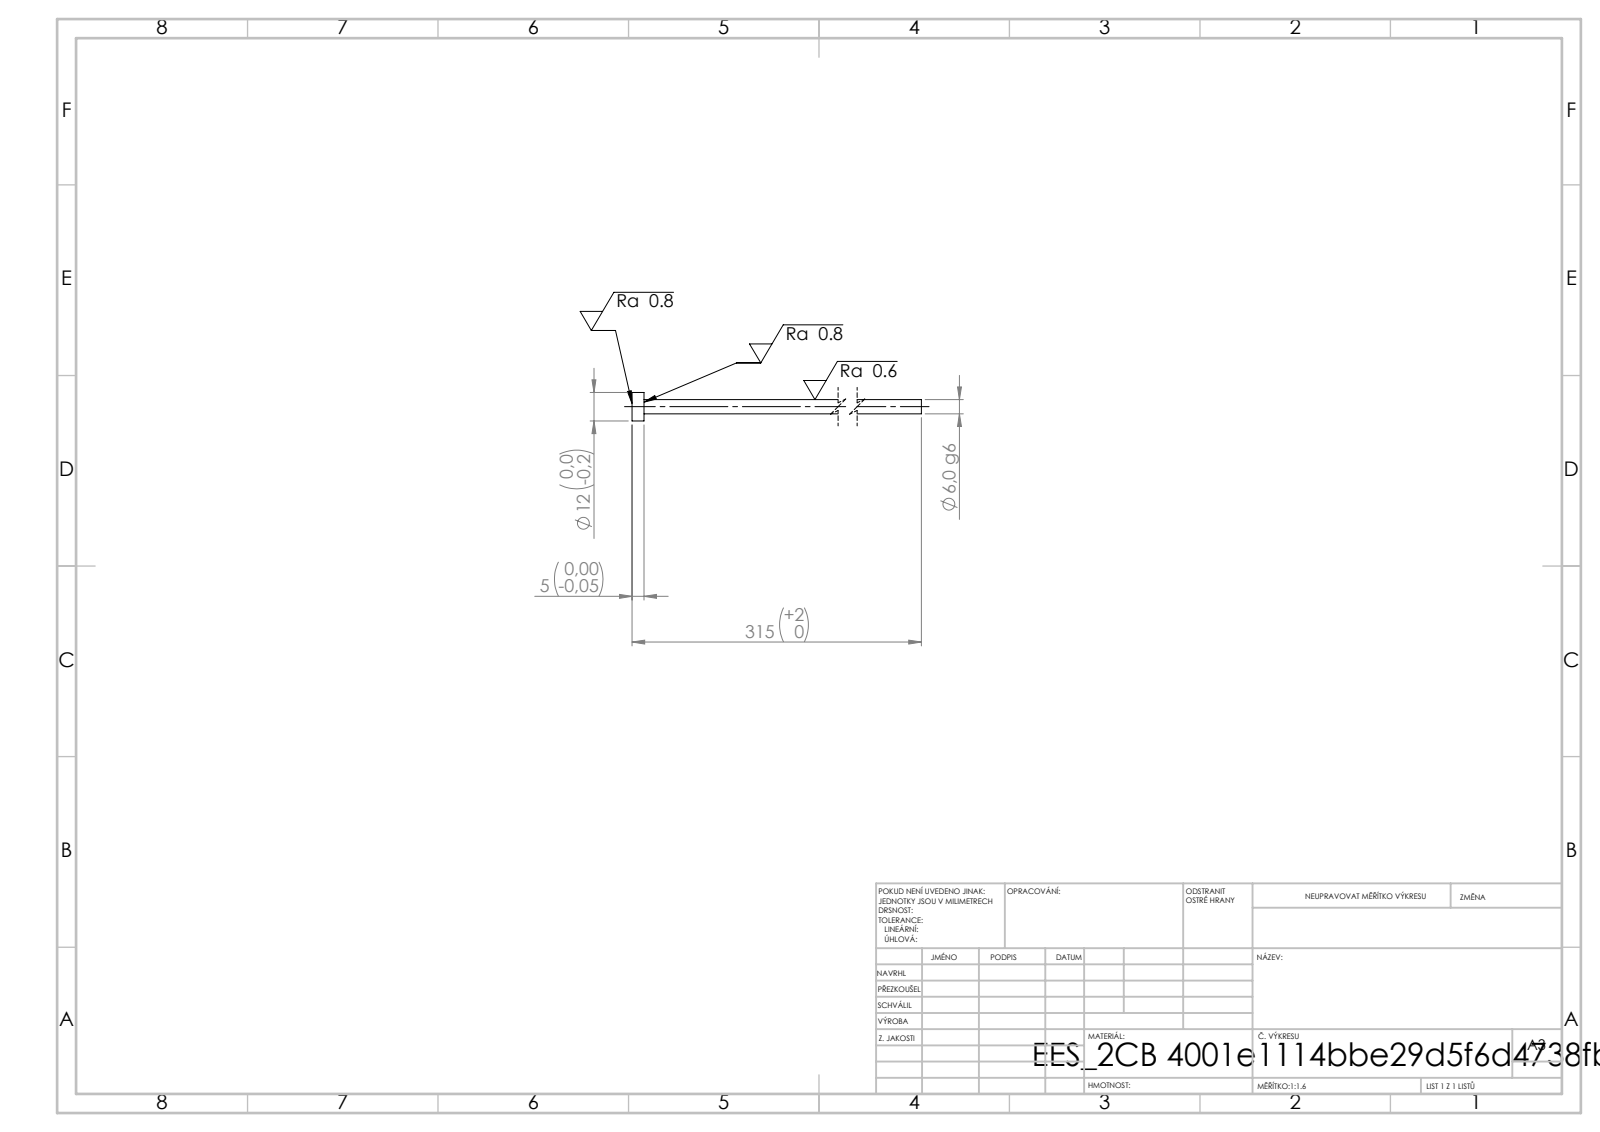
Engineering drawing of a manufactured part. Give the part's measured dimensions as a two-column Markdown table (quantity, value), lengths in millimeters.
| quantity | value |
| --- | --- |
| STEP written by | SolidWorks 2019 (CONFIG_CONTROL_DESIGN) |
| units | millimeters |
| bodies | 1 solid, 7 faces (3 planar, 4 cylindrical, 0 other) |
| overall size | 315 × 12 × 12 |
| volume | 9 331 mm³ |
| surface area | 6 258 mm² |
| round bosses / shafts (diameter × count) | 12 × 1, 6 × 1 |
| main face-to-face distances | 5, 315, 310 |
